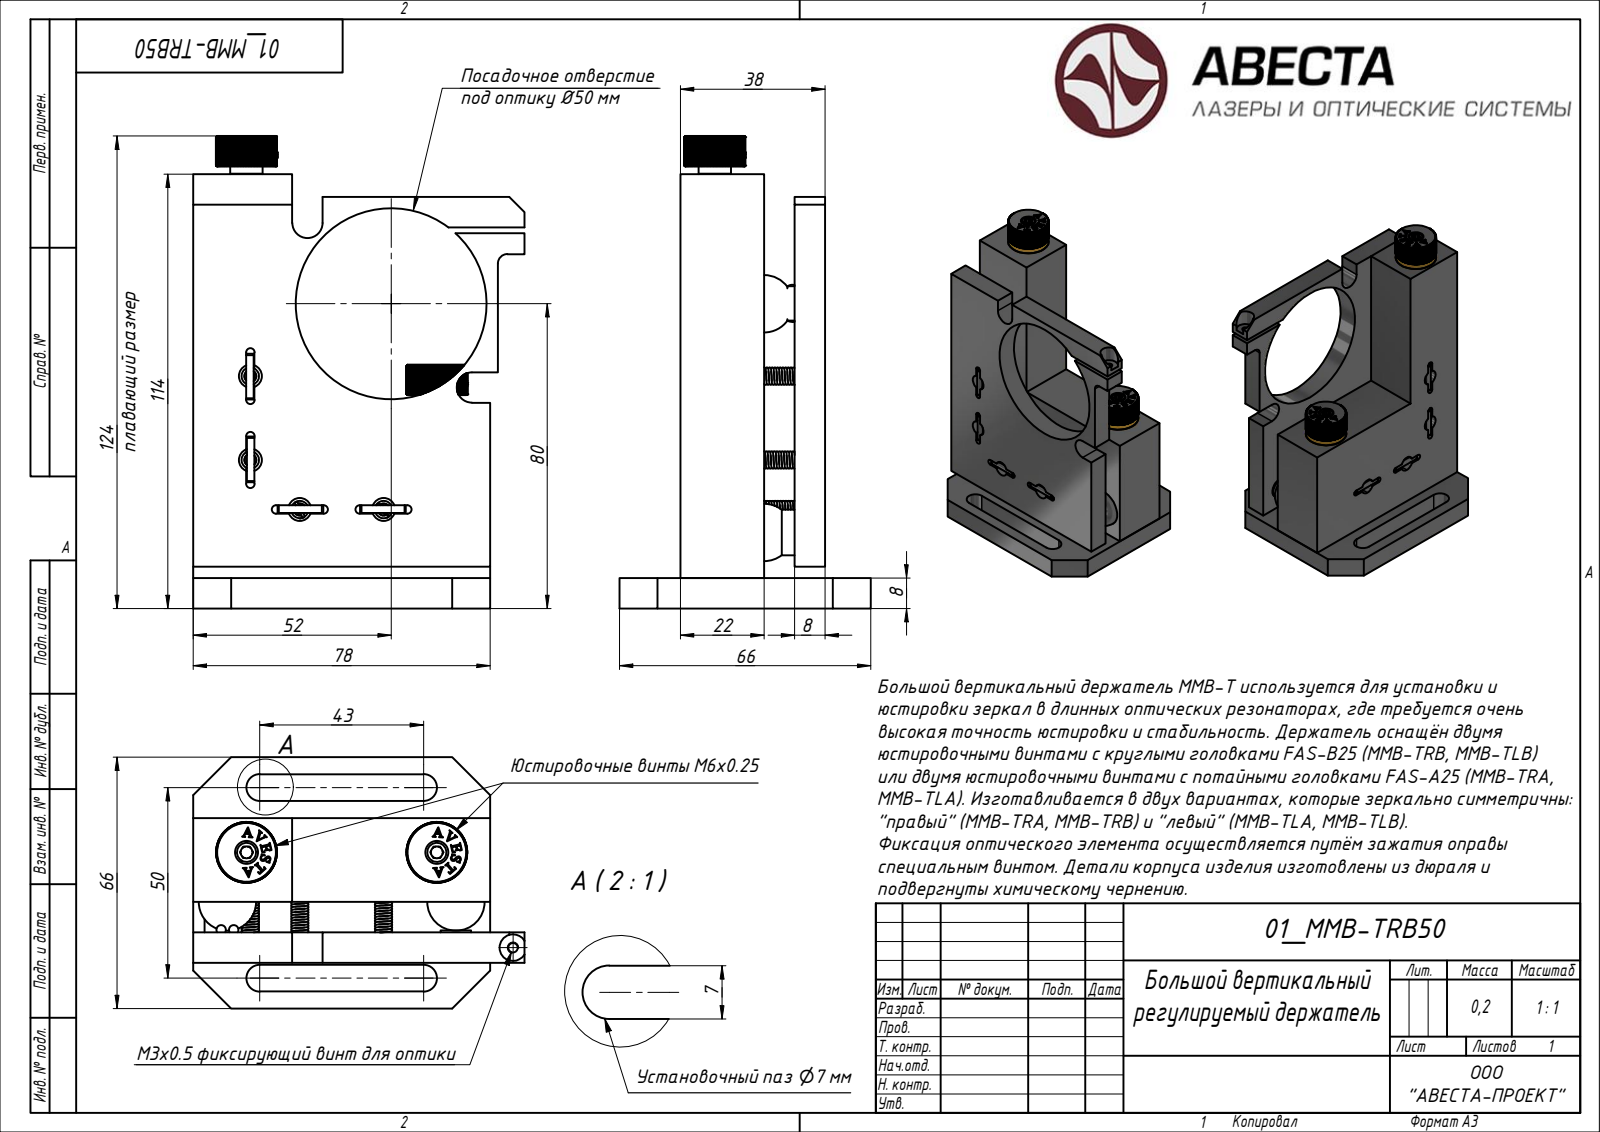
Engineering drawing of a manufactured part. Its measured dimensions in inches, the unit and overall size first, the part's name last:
Units: inches
Overall size (bounding box): 7.91 × 4.884 × 2.604
Main face-to-face distances: 0.315, 1.496, 0.63, 1.181, 0.32, 0.309, 0.866, 4.485, 1.502, 1.491
Volume: 22.35 in³ · Surface area: 195.6 in²
Bodies: 46 solids, 1133 faces (522 planar, 0 cylindrical, 611 other)
Part name (STEP PRODUCT): 01_MMB-TRB50
STEP written by: ST-DEVELOPER v15 (AUTOMOTIVE_DESIGN)
